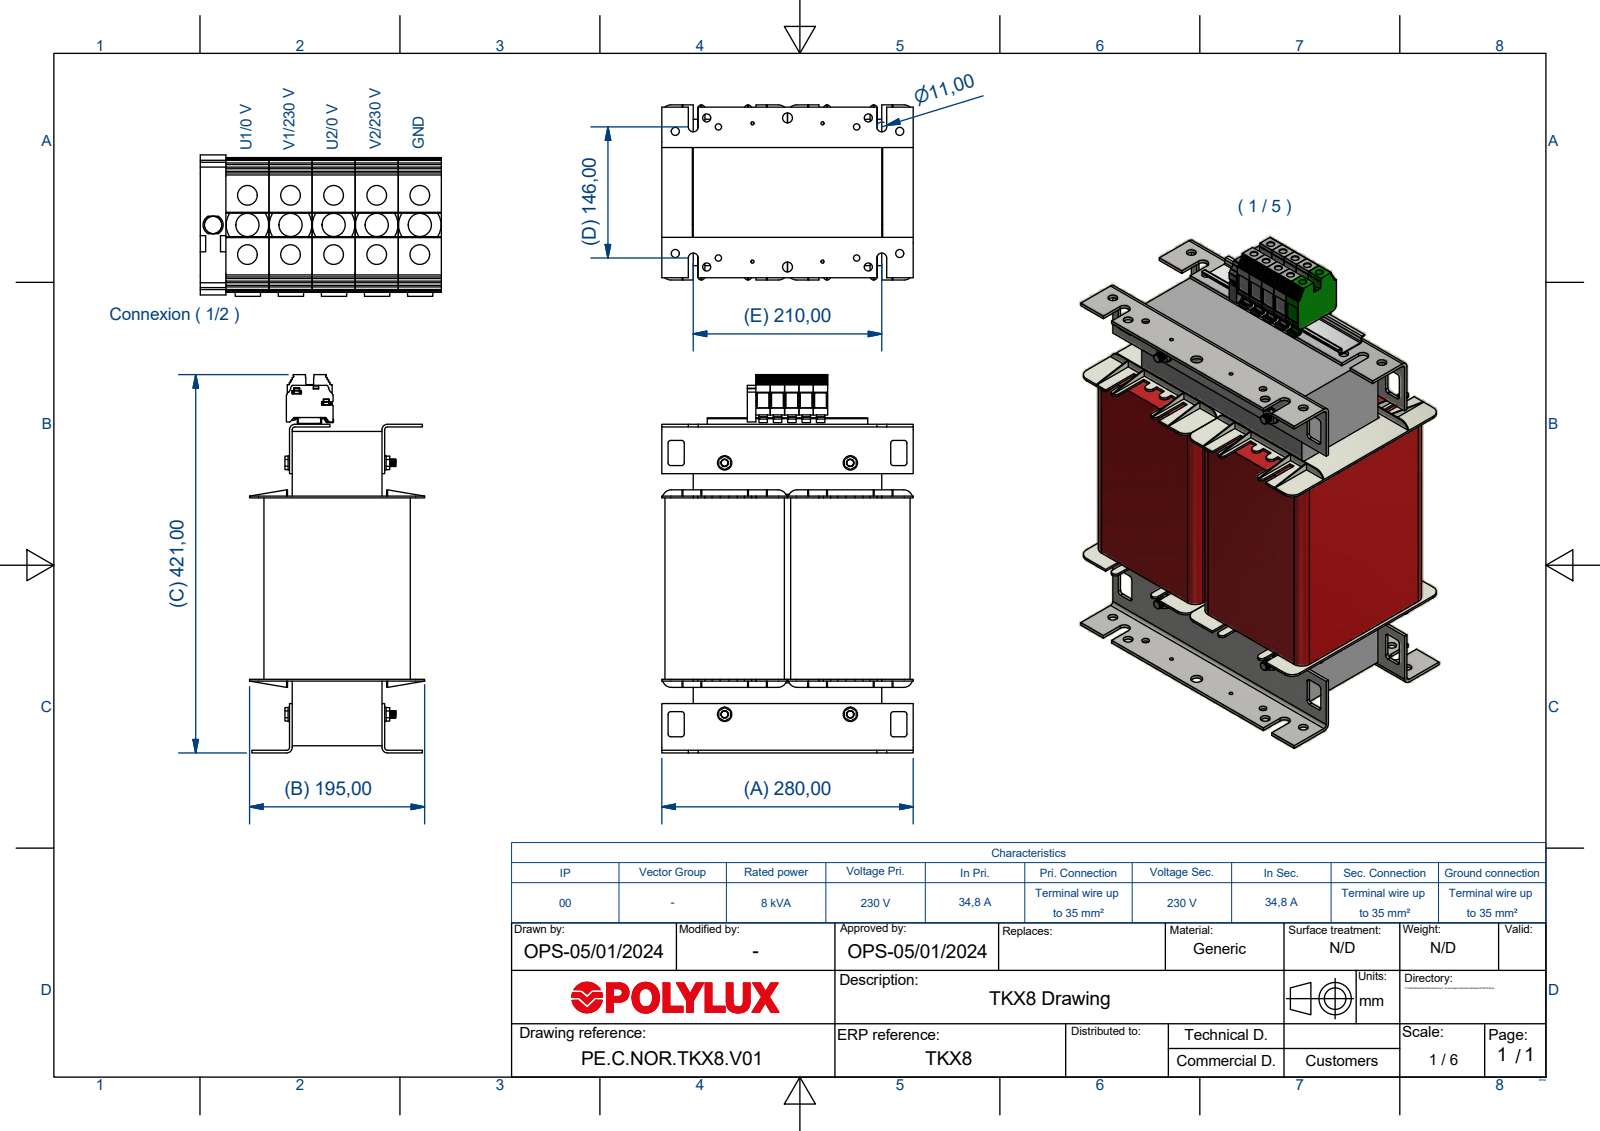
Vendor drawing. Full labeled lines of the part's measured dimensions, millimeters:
Part name (STEP PRODUCT): TKX8
STEP written by: Autodesk Inventor 2018 (AUTOMOTIVE_DESIGN)
Units: millimetres
Bodies: 32 solids, 1972 faces (1476 planar, 469 cylindrical, 27 other)
Overall size (bounding box): 421.3 × 280 × 195
Volume: 12 240 000 mm³ · Surface area: 1 484 000 mm²
Round holes (diameter × count): ⌀9 ×12, ⌀7.3 ×10, ⌀3.5 ×6, ⌀7 ×6, ⌀8.6 ×5, ⌀6.65 ×4, ⌀8.4 ×4, ⌀12 ×4, ⌀11 ×3
Round bosses / shafts (diameter × count): ⌀16 ×4, ⌀8 ×4
Partial cylindrical surfaces — rounded edges, fillets, slot ends (radius × count): R0.5 ×24, R10 ×24, R3 ×20, R1 ×16, R0.2 ×11, R2 ×9, R4 ×8, R4.5 ×8
Main face-to-face distances: 3, 140, 2, 28.5, 31.5, 103, 1, 30.5, 74, 104.5
Hole centre spacings: 103, 16.4, 38.08, 38.21, 39.46, 48.26, 51.35, 77.65
